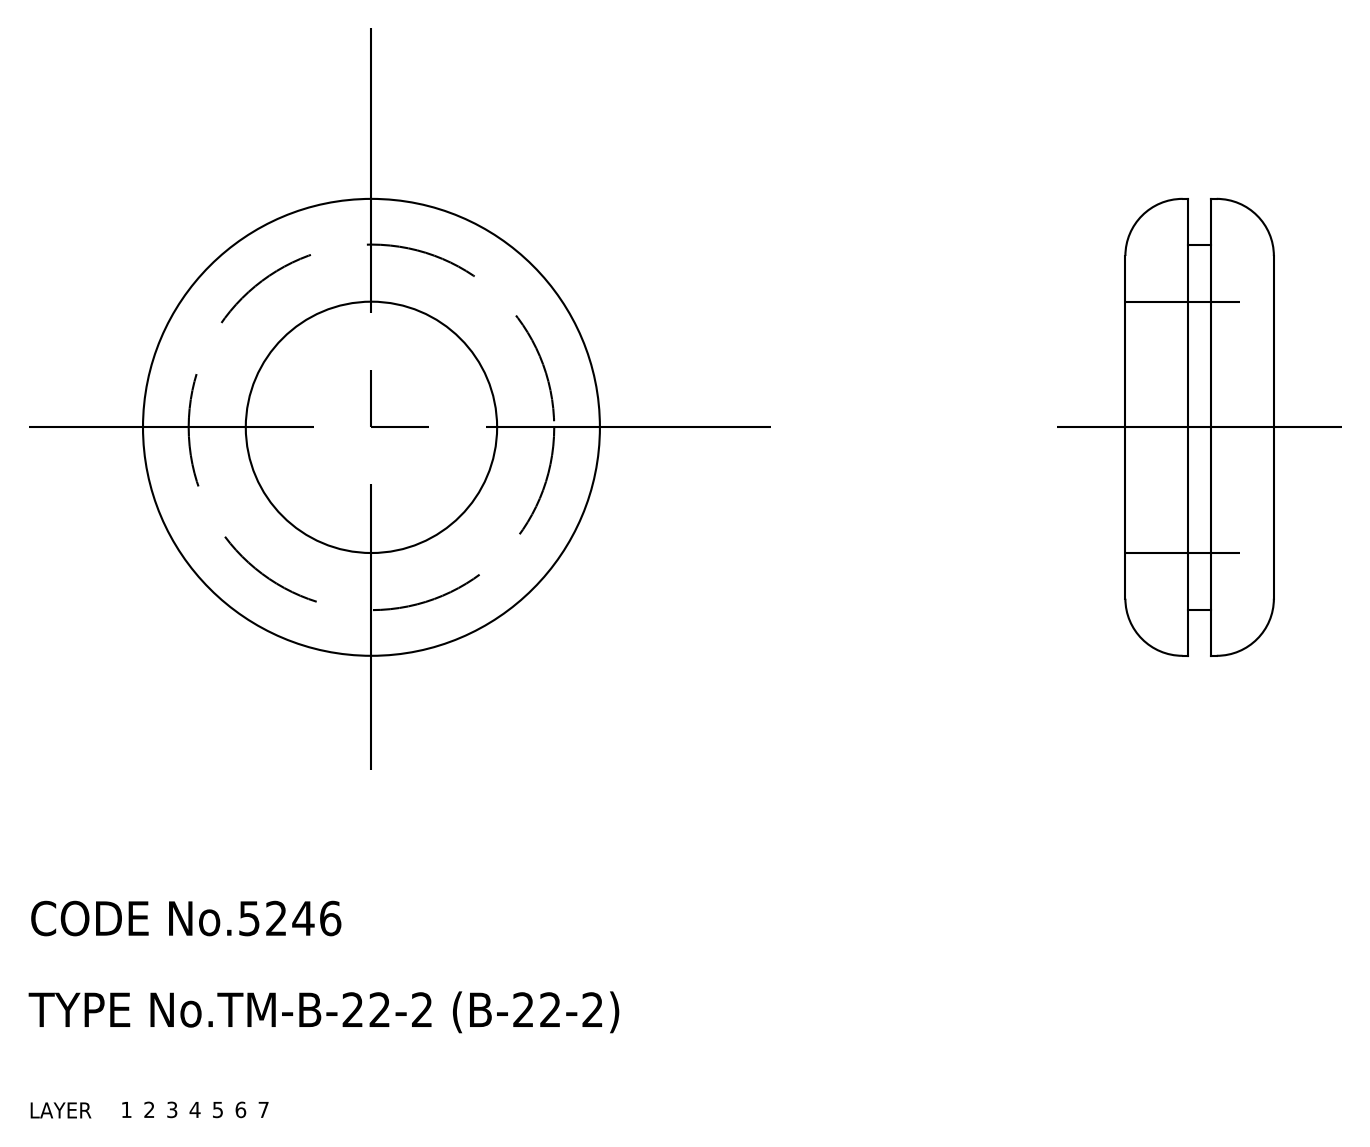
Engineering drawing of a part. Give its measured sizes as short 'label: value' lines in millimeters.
name: grommet
written by: CADfix (AUTOMOTIVE_DESIGN)
unit: mm
bodies: 1 solid, 16 faces (0 planar, 0 cylindrical, 16 other)
size: 40 × 40 × 13
volume: 9 242 mm³; area: 4 580 mm²
